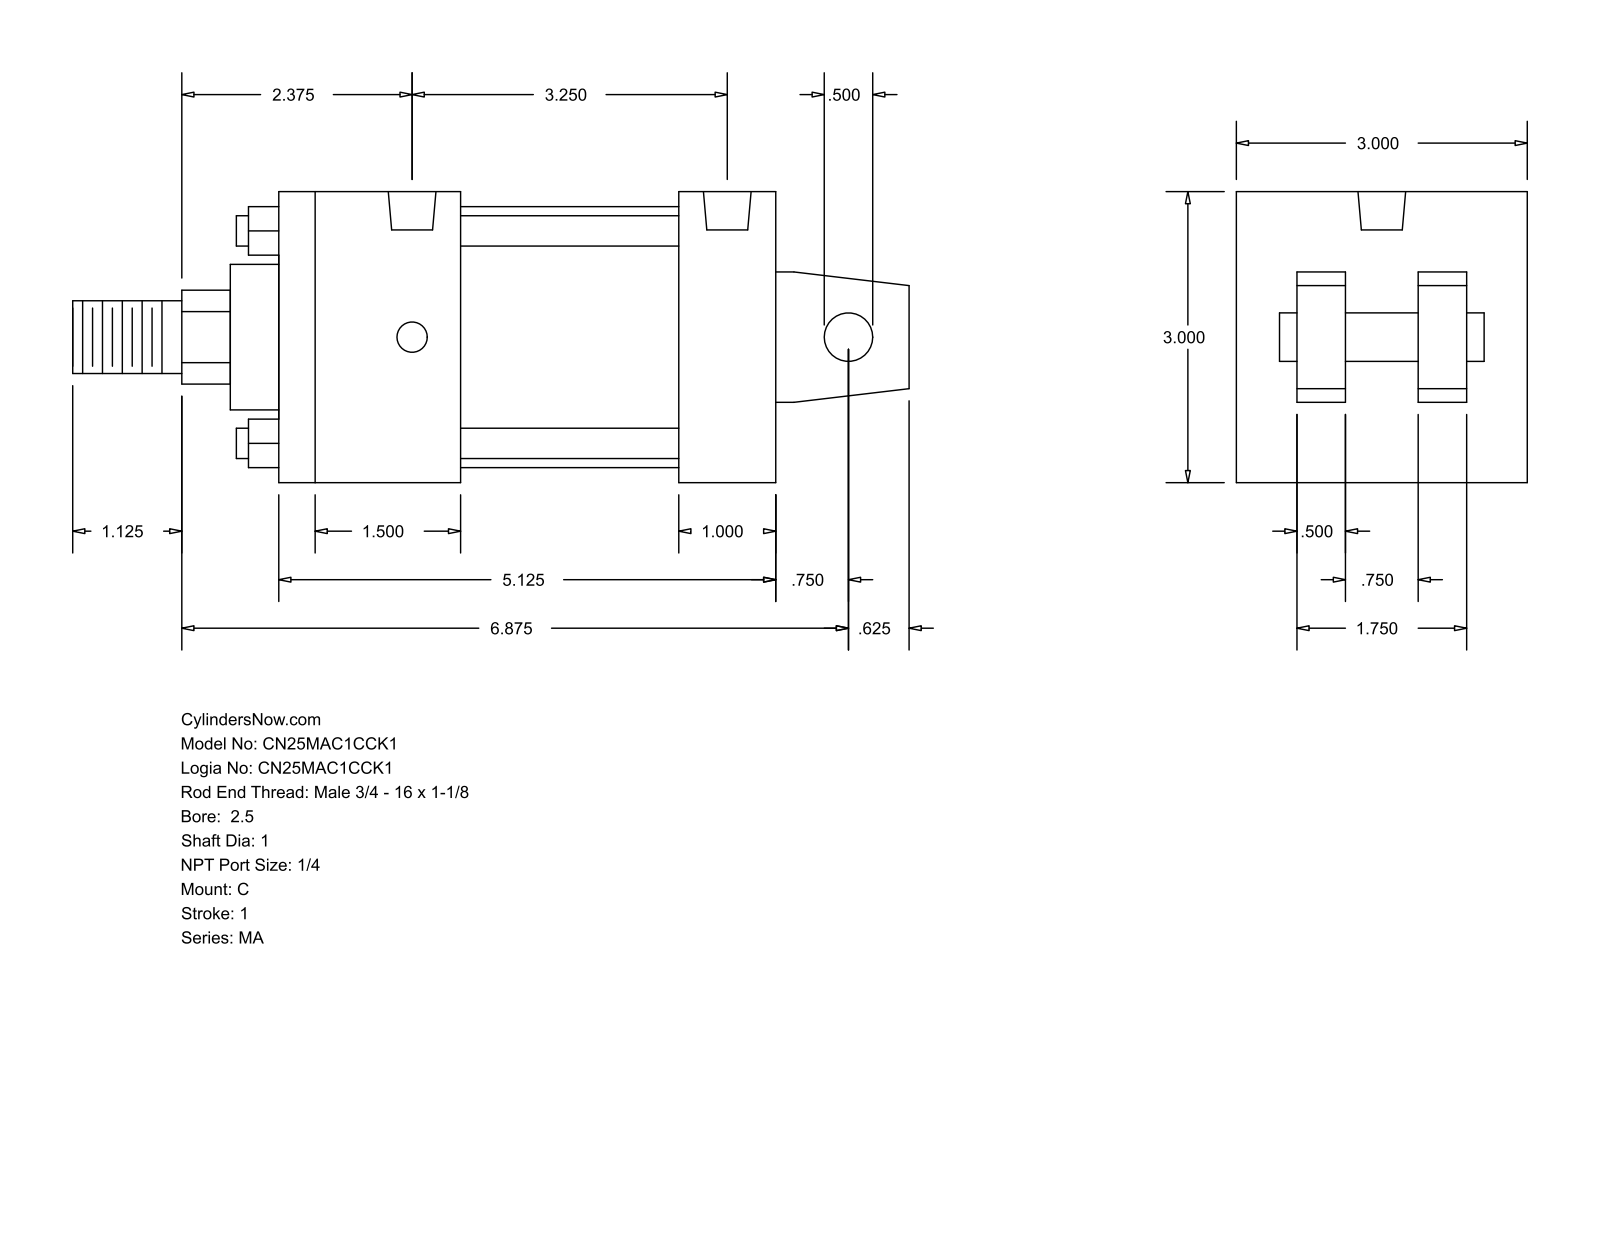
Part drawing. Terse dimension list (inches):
name: MA_C__0250_1
written by: GSSL Pune (CONFIG_CONTROL_DESIGN)
unit: in
bodies: 0 solids, 103 faces (76 planar, 27 cylindrical, 0 other)
size: 8.625 × 3 × 3
holes: 4× ⌀0.313, 2× ⌀0.492
bosses: 4× ⌀0.313, 1× ⌀2.69, 1× ⌀1.5, 1× ⌀1, 1× ⌀0.75, 1× ⌀0.5
rounds: 1× R0.484
face distances: 3, 1.875, 5.125, 0.5, 2.375, 0.625, 1.125, 4.125, 2.25, 3.25
hole spacings: 3.25
